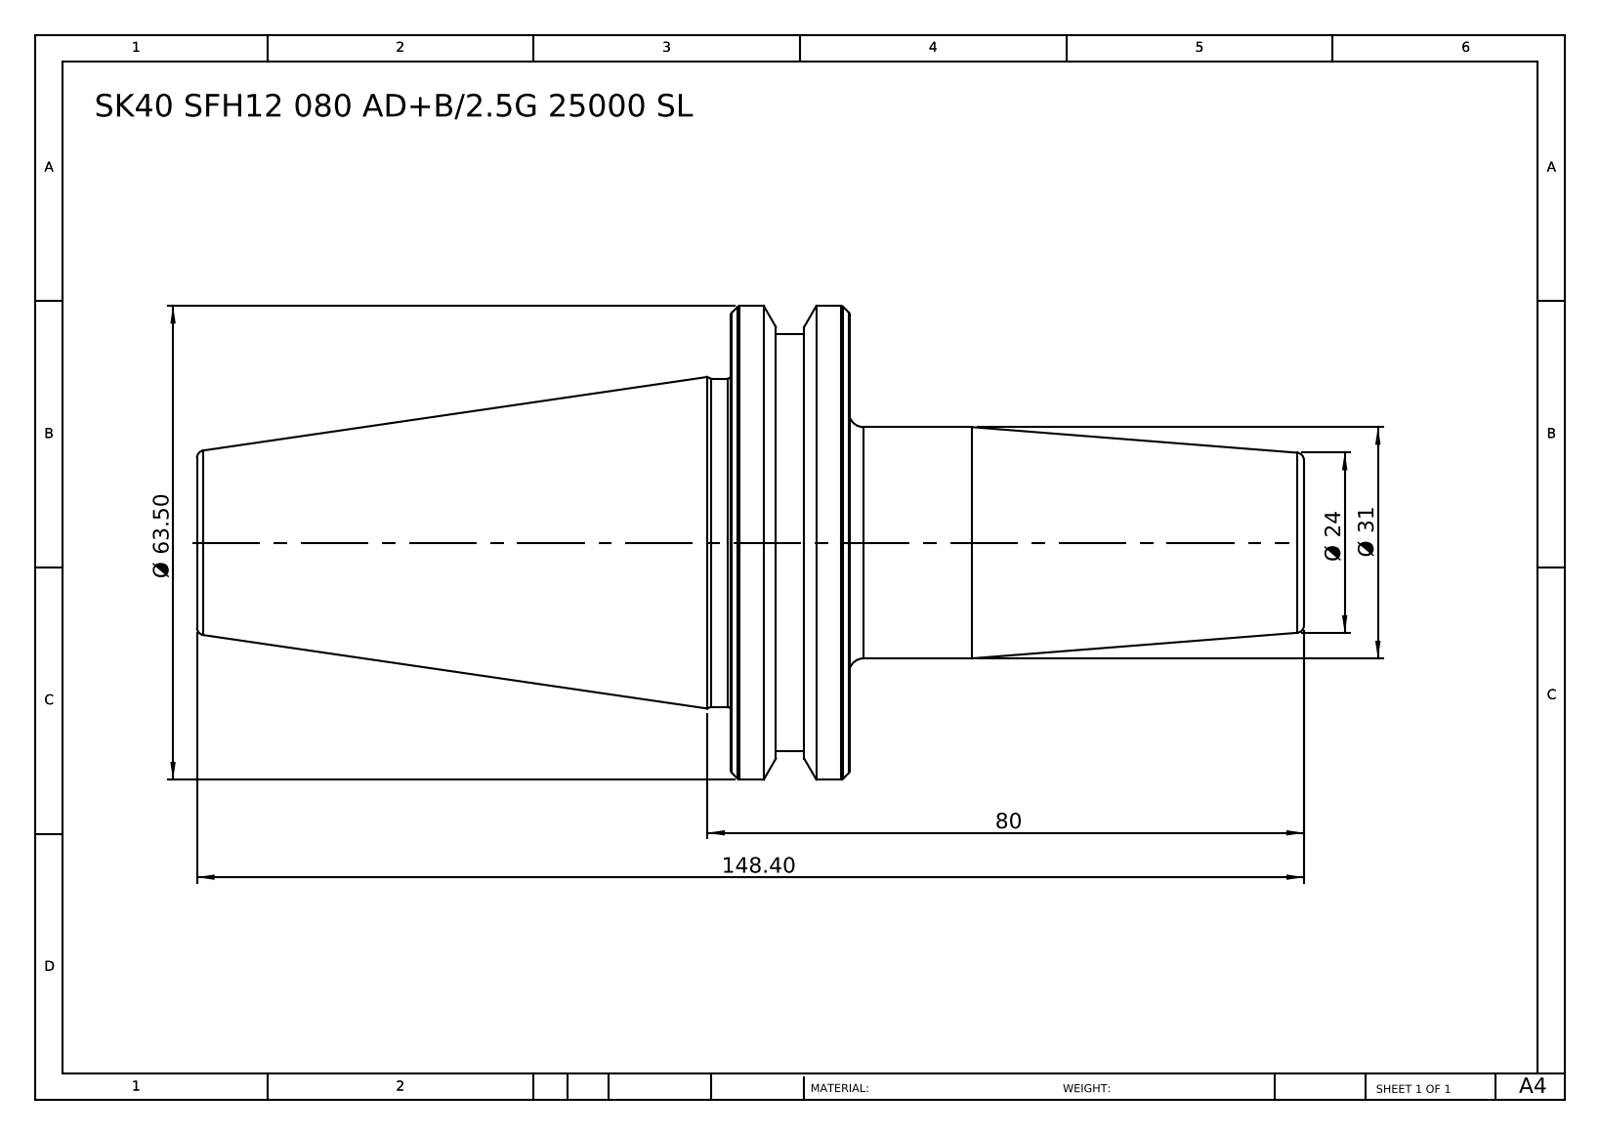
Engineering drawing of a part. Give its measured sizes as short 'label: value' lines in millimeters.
name: SK40 SFH12 80 AD+B-2.5G 25000 SL
written by: SolidWorks 2014 (CONFIG_CONTROL_DESIGN)
unit: mm
bodies: 1 solid, 46 faces (6 planar, 10 cylindrical, 30 other)
size: 148.4 × 63.5 × 63.5
volume: 156 107 mm³; area: 21 979 mm²
bosses: 1× ⌀63.5, 1× ⌀56, 1× ⌀44, 1× ⌀31
face distances: 15.9, 87.5, 71.6, 60.9, 76.8, 148.4, 67, 6.1, 9.8, 81.4
